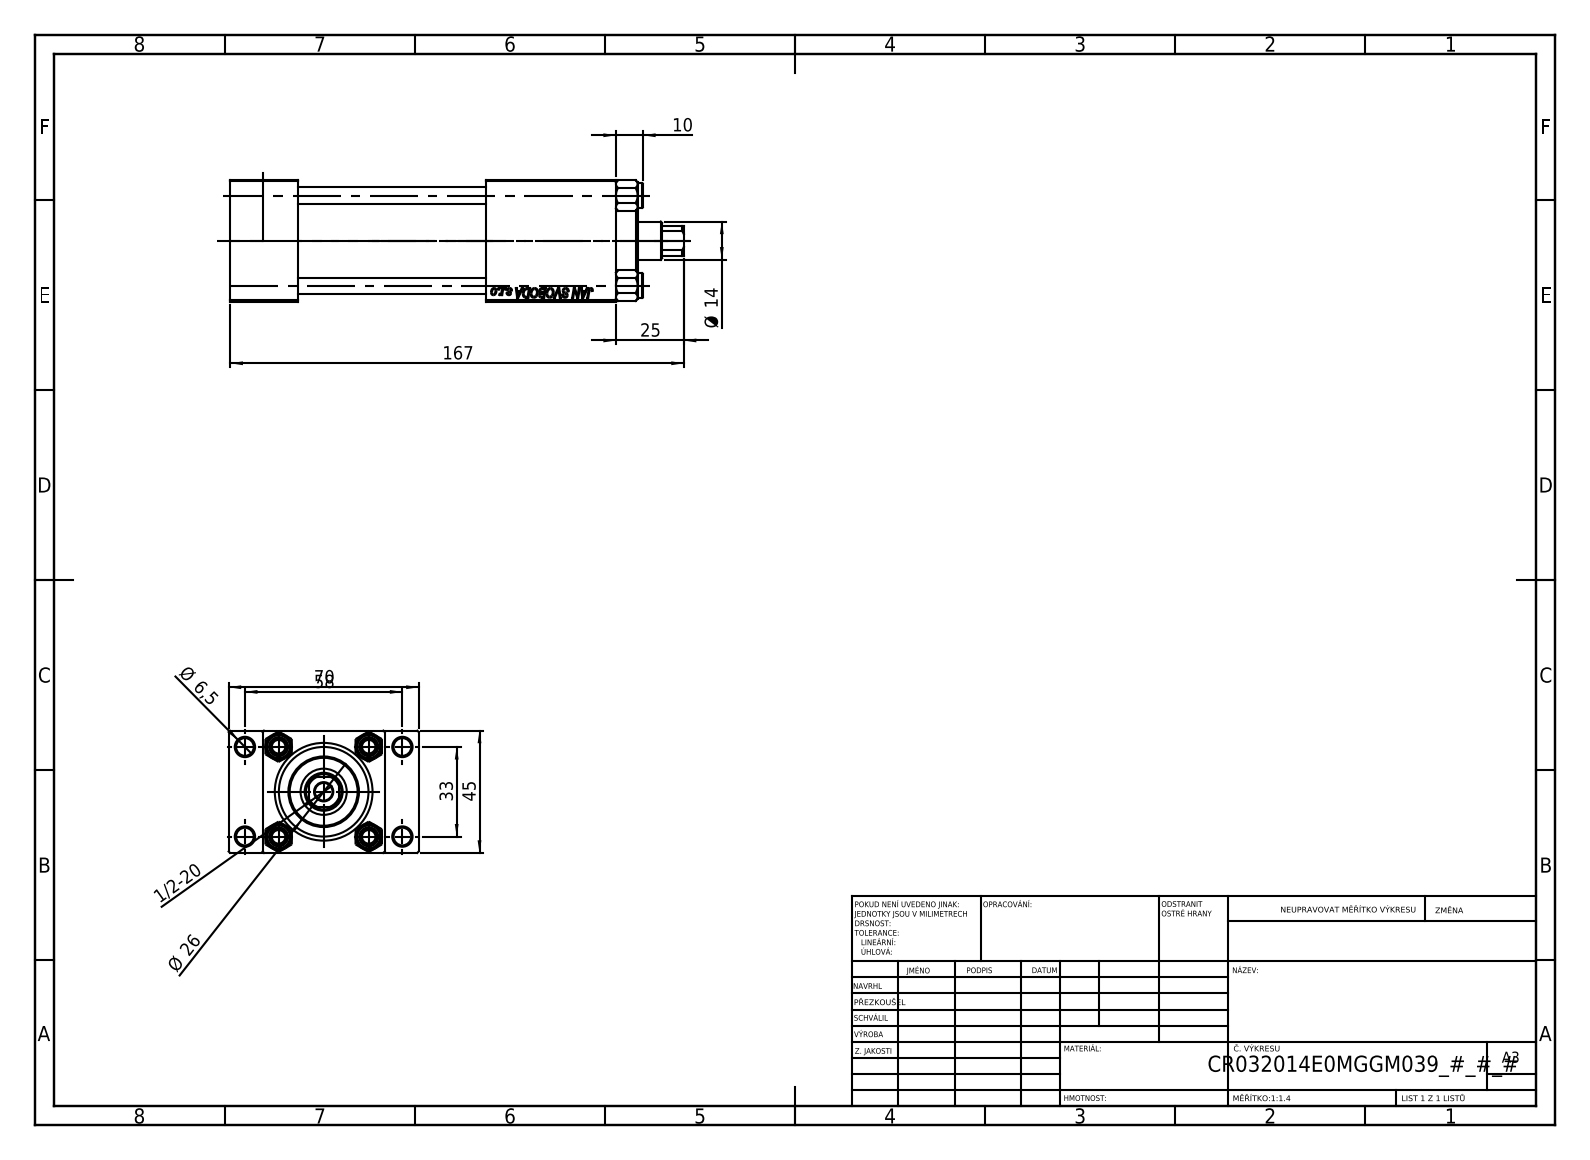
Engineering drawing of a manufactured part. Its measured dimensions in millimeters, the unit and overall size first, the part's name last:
Units: millimetres
Overall size (bounding box): 167 × 70 × 45
Round holes (diameter × count): ⌀6.5 ×5, ⌀6 ×4, ⌀7 ×2, ⌀13.16 ×2, ⌀20 ×2, ⌀14 ×1, ⌀17 ×1, ⌀24 ×1, ⌀32 ×1, ⌀33 ×1
Round bosses / shafts (diameter × count): ⌀9 ×4, ⌀38 ×1, ⌀26 ×1
Partial cylindrical surfaces — rounded edges, fillets, slot ends (radius × count): R6.5 ×1
Main face-to-face distances: 45, 25, 12.5, 57.5, 142, 117, 70, 94, 69, 48
Hole centre spacings: 12.4, 23.48, 33.2, 33.37, 35.35, 45.6, 56.35, 33
Volume: 231 414 mm³ · Surface area: 82 519 mm²
Bodies: 11 solids, 1136 faces (497 planar, 87 cylindrical, 552 other)
Part name (STEP PRODUCT): V215CR_TYCINKA_E; V215CR_E_Body; V215CR_VCP_E; V215_VC_A (+1 more)
STEP written by: SolidWorks 2019 (CONFIG_CONTROL_DESIGN)
